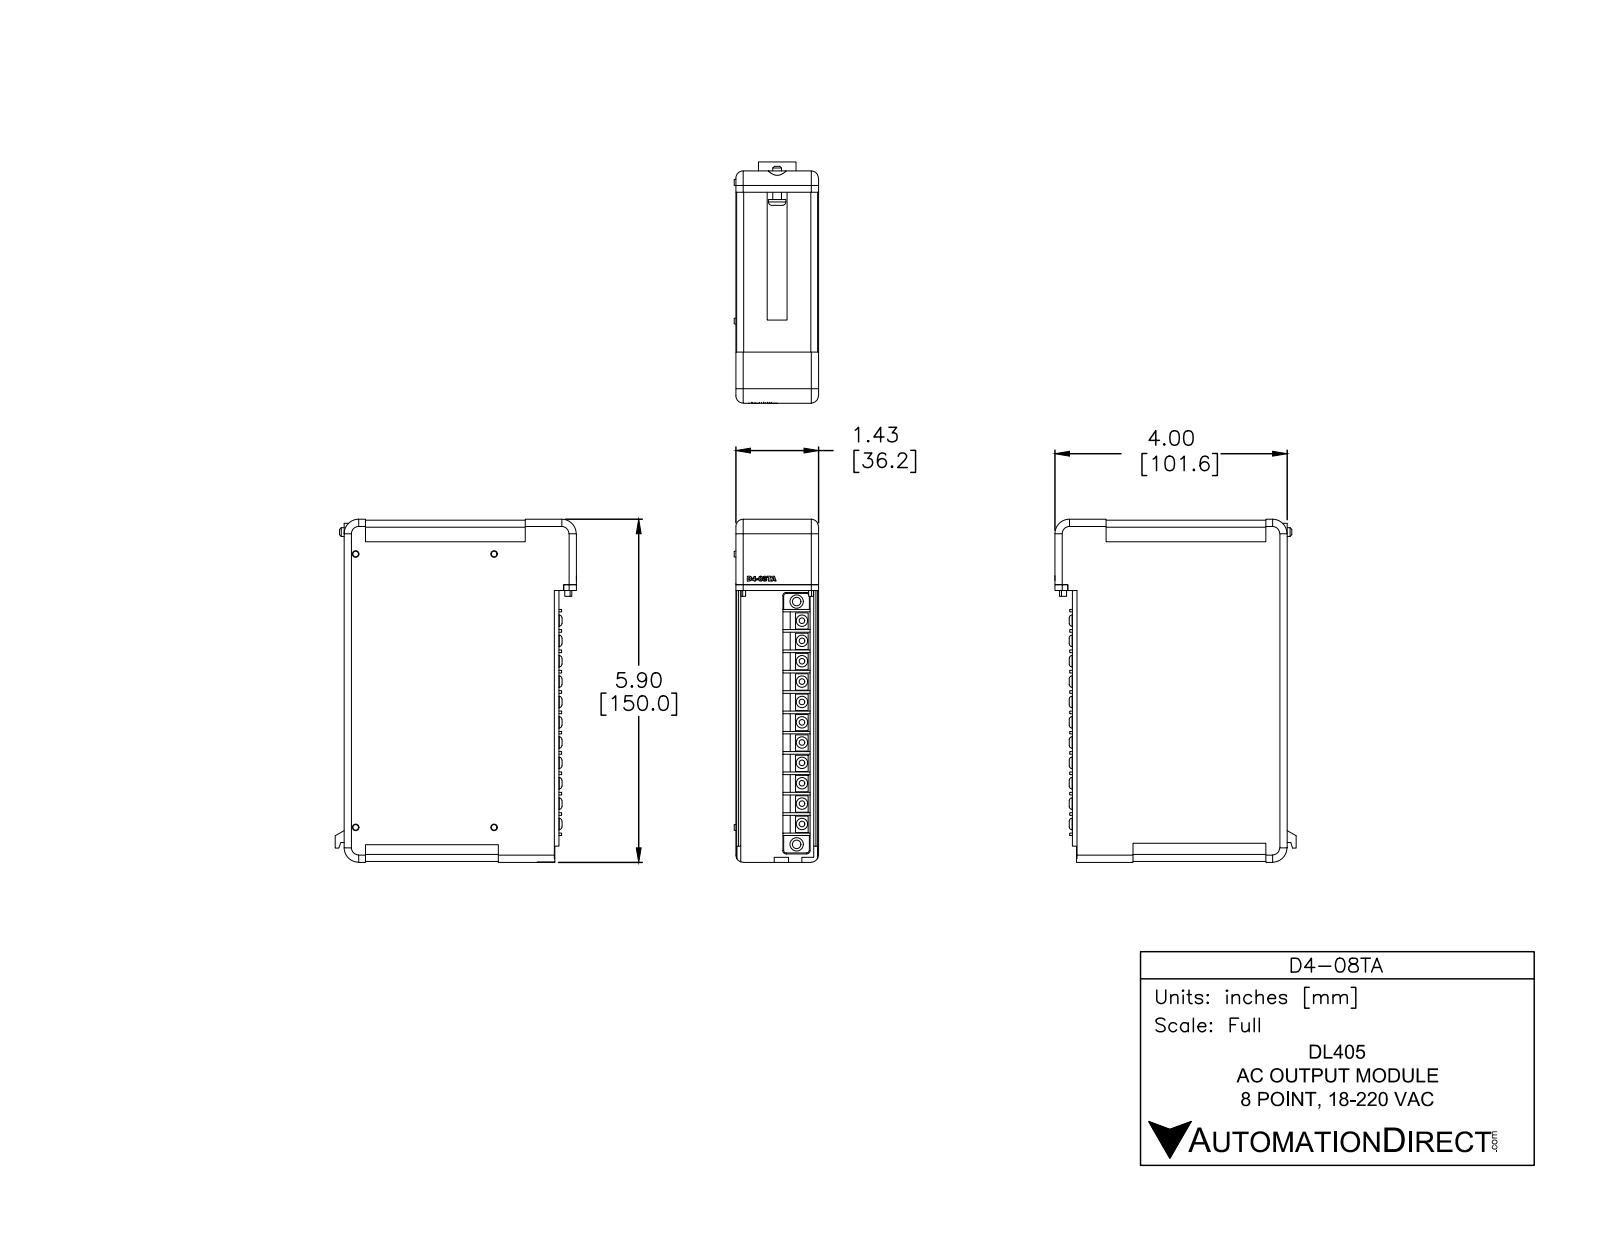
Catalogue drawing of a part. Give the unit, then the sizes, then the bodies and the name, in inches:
Units: inches
Overall size (bounding box): 5.905 × 4.156 × 1.455
Round bosses / shafts (diameter × count): ⌀0.2 ×11, ⌀0.229 ×2, ⌀0.3 ×1, ⌀0.15 ×1
Partial cylindrical surfaces — rounded edges, fillets, slot ends (radius × count): R0.125 ×8, R0.015 ×6, R0.06 ×4, R0.12 ×4, R0.25 ×3, R0.03 ×2, R0.151 ×1, R0.171 ×1
Main face-to-face distances: 1.425, 0.015, 3.325, 0.085, 1.34, 5.875, 0.07, 0.2, 1.41, 1.325
Volume: 29.11 in³ · Surface area: 85.81 in²
Bodies: 10 solids, 439 faces (290 planar, 71 cylindrical, 78 other)
Part name (STEP PRODUCT): D4-08TA
STEP written by: SolidWorks 2014 (AUTOMOTIVE_DESIGN)
